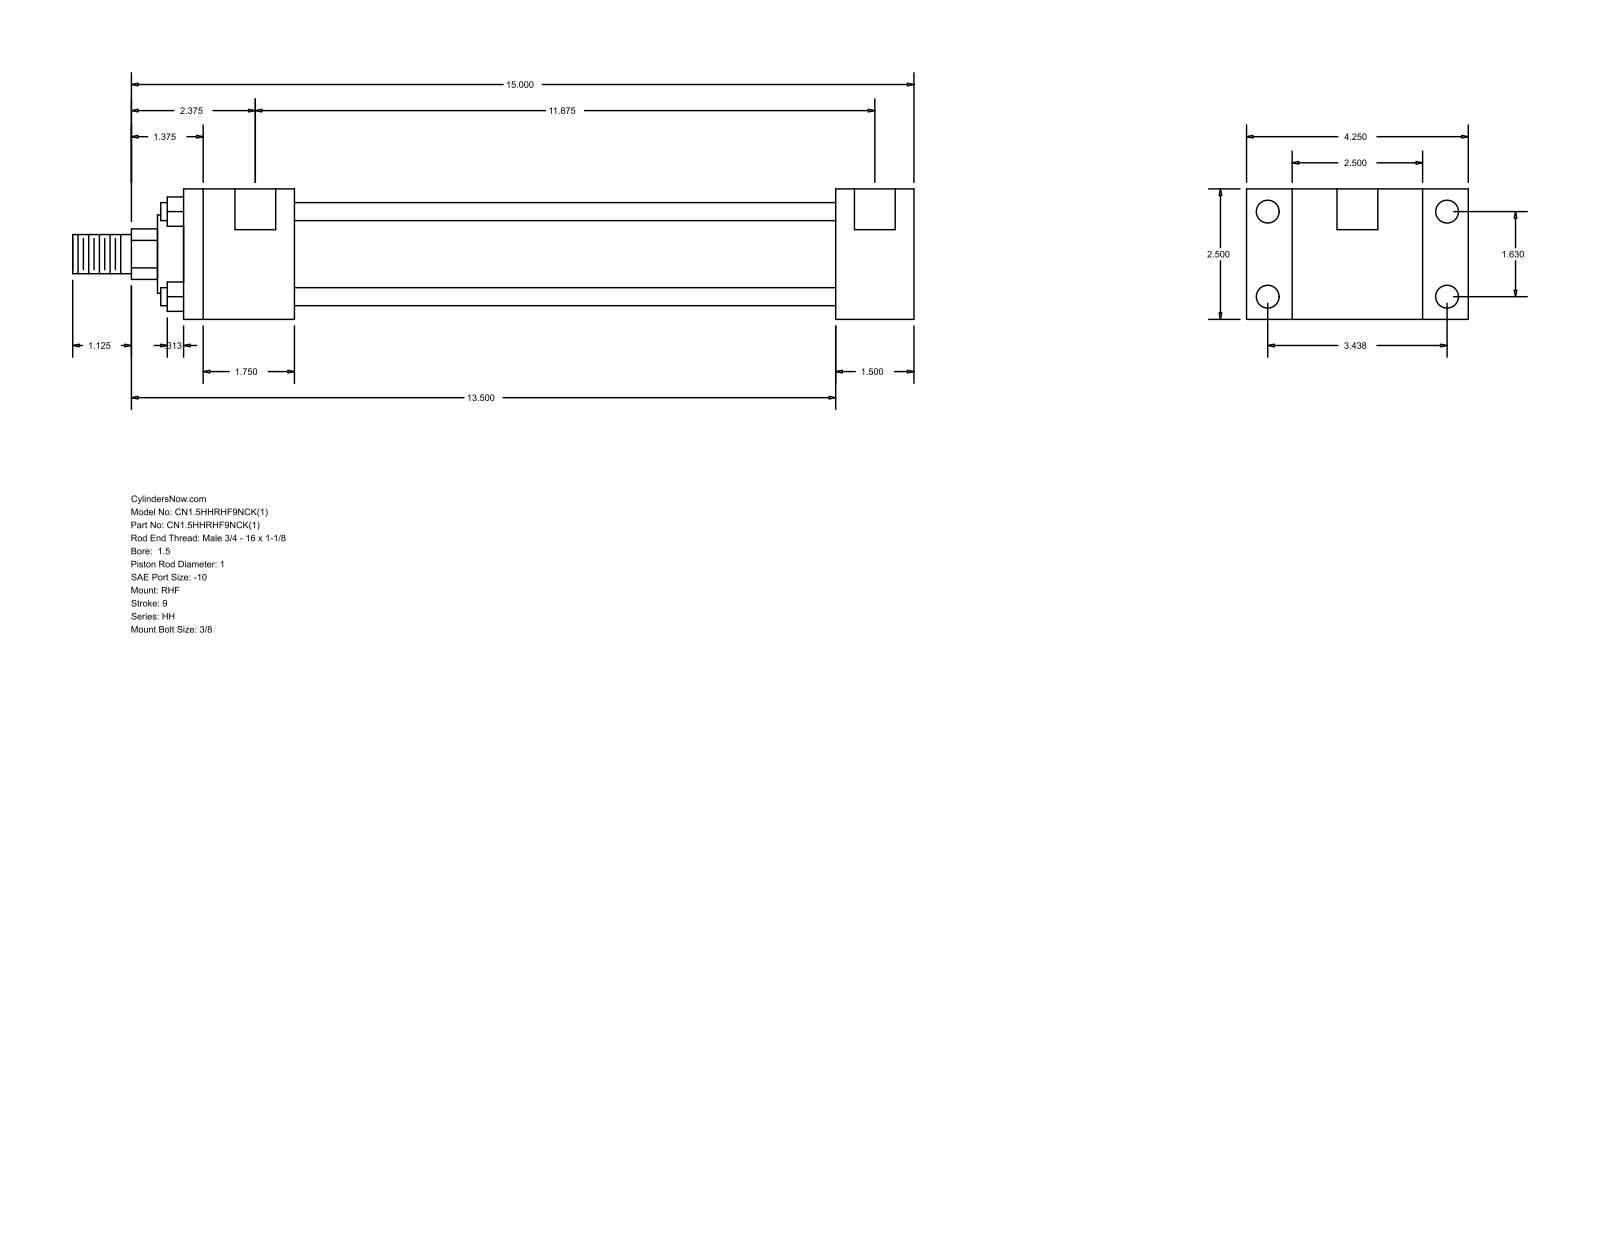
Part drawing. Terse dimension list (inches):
name: HH_RHF__0150_1
written by: GSSL Pune (CONFIG_CONTROL_DESIGN)
unit: in
bodies: 0 solids, 88 faces (60 planar, 28 cylindrical, 0 other)
size: 16.125 × 4.25 × 2.5
holes: 4× ⌀0.219, 4× ⌀0.438, 2× ⌀0.781
bosses: 4× ⌀0.345, 1× ⌀1.75, 1× ⌀1.5, 1× ⌀1, 1× ⌀0.75
rounds: 1× R0.484
face distances: 2.5, 0.875, 3.375, 1.5, 4.25, 10.375, 11.875, 2.125, 12.5, 14
hole spacings: 0.063, 1.63, 3.438, 3.805, 11.937, 12, 11.875
